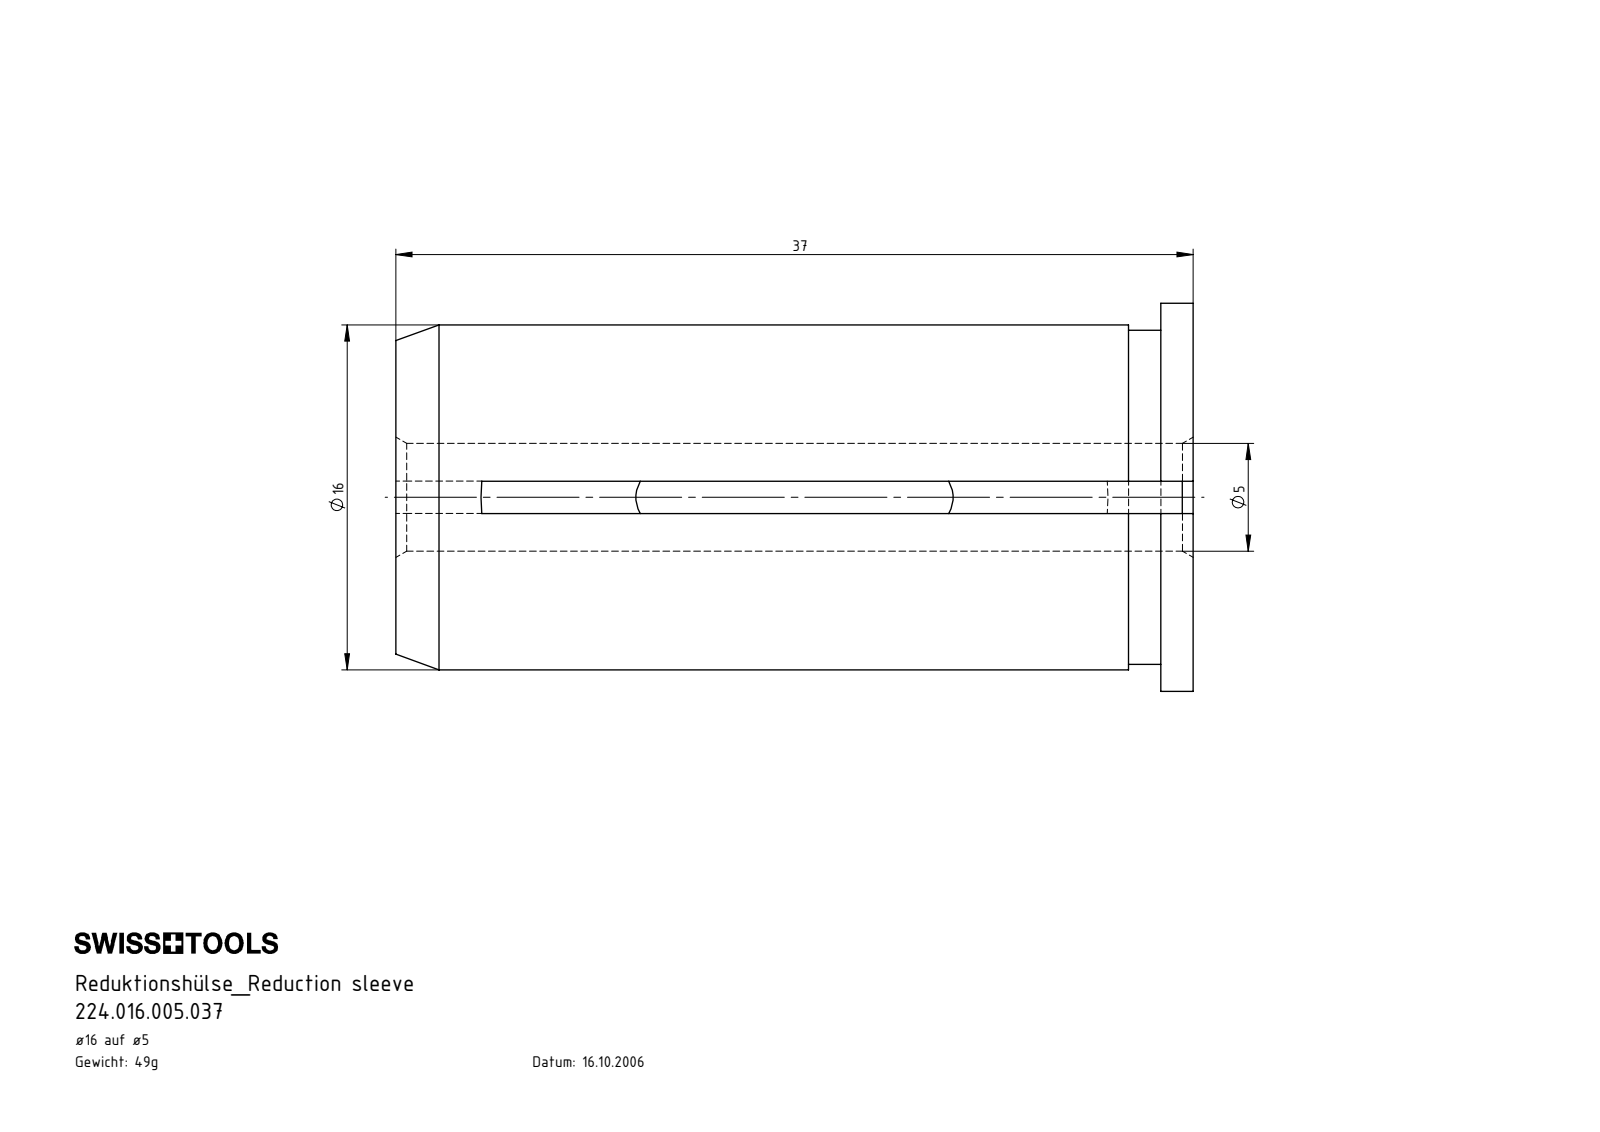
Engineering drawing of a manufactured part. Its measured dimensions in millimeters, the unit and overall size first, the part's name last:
Units: millimetres
Overall size (bounding box): 37 × 18 × 17.97
Round holes (diameter × count): ⌀5 ×1
Round bosses / shafts (diameter × count): ⌀18 ×1, ⌀16 ×1, ⌀15.5 ×1
Partial cylindrical surfaces — rounded edges, fillets, slot ends (radius × count): R31.5 ×2
Main face-to-face distances: 1.5, 37, 35.5, 34, 3
Volume: 6 242 mm³ · Surface area: 3 397 mm²
Bodies: 1 solid, 17 faces (8 planar, 6 cylindrical, 3 other)
Part name (STEP PRODUCT): U05.U16.001.037
STEP written by: SolidWorks 2017 (AUTOMOTIVE_DESIGN)
